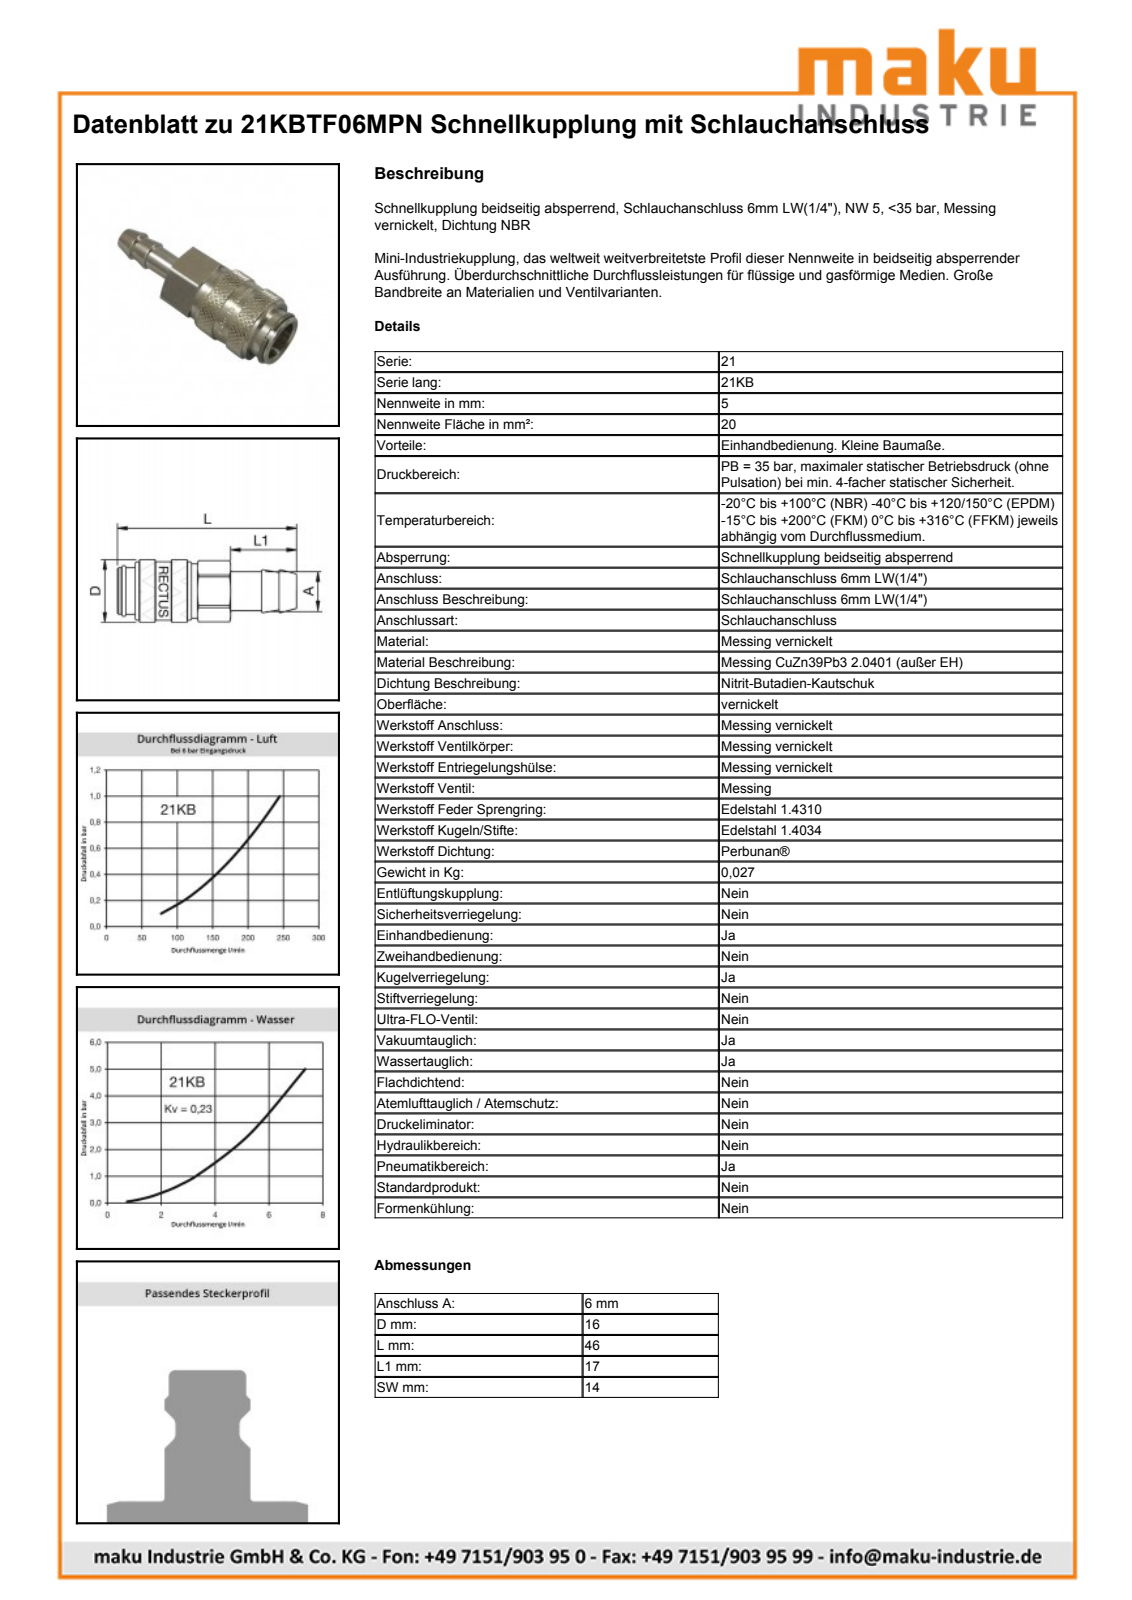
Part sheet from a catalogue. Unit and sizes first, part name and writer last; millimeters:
Units: millimetres
Overall size (bounding box): 46.15 × 16.15 × 16.15
Round holes (diameter × count): ⌀12.15 ×1, ⌀14 ×1
Round bosses / shafts (diameter × count): ⌀16.15 ×1, ⌀15.1 ×1, ⌀12 ×1, ⌀11.4 ×1, ⌀11.15 ×1, ⌀11.15 ×1, ⌀6.05 ×1
Partial cylindrical surfaces — rounded edges, fillets, slot ends (radius × count): R7.45 ×1, R7.9 ×1
Main face-to-face distances: 14, 29.15, 4.5, 24.65, 11.8, 7.3, 17.35, 16.15, 11.65, 4.35
Volume: 5 184 mm³ · Surface area: 3 545 mm²
Bodies: 2 solids, 463 faces (151 planar, 62 cylindrical, 250 other)
Part name (STEP PRODUCT): D105337
STEP written by: Autodesk Inventor 2013 (AUTOMOTIVE_DESIGN)
